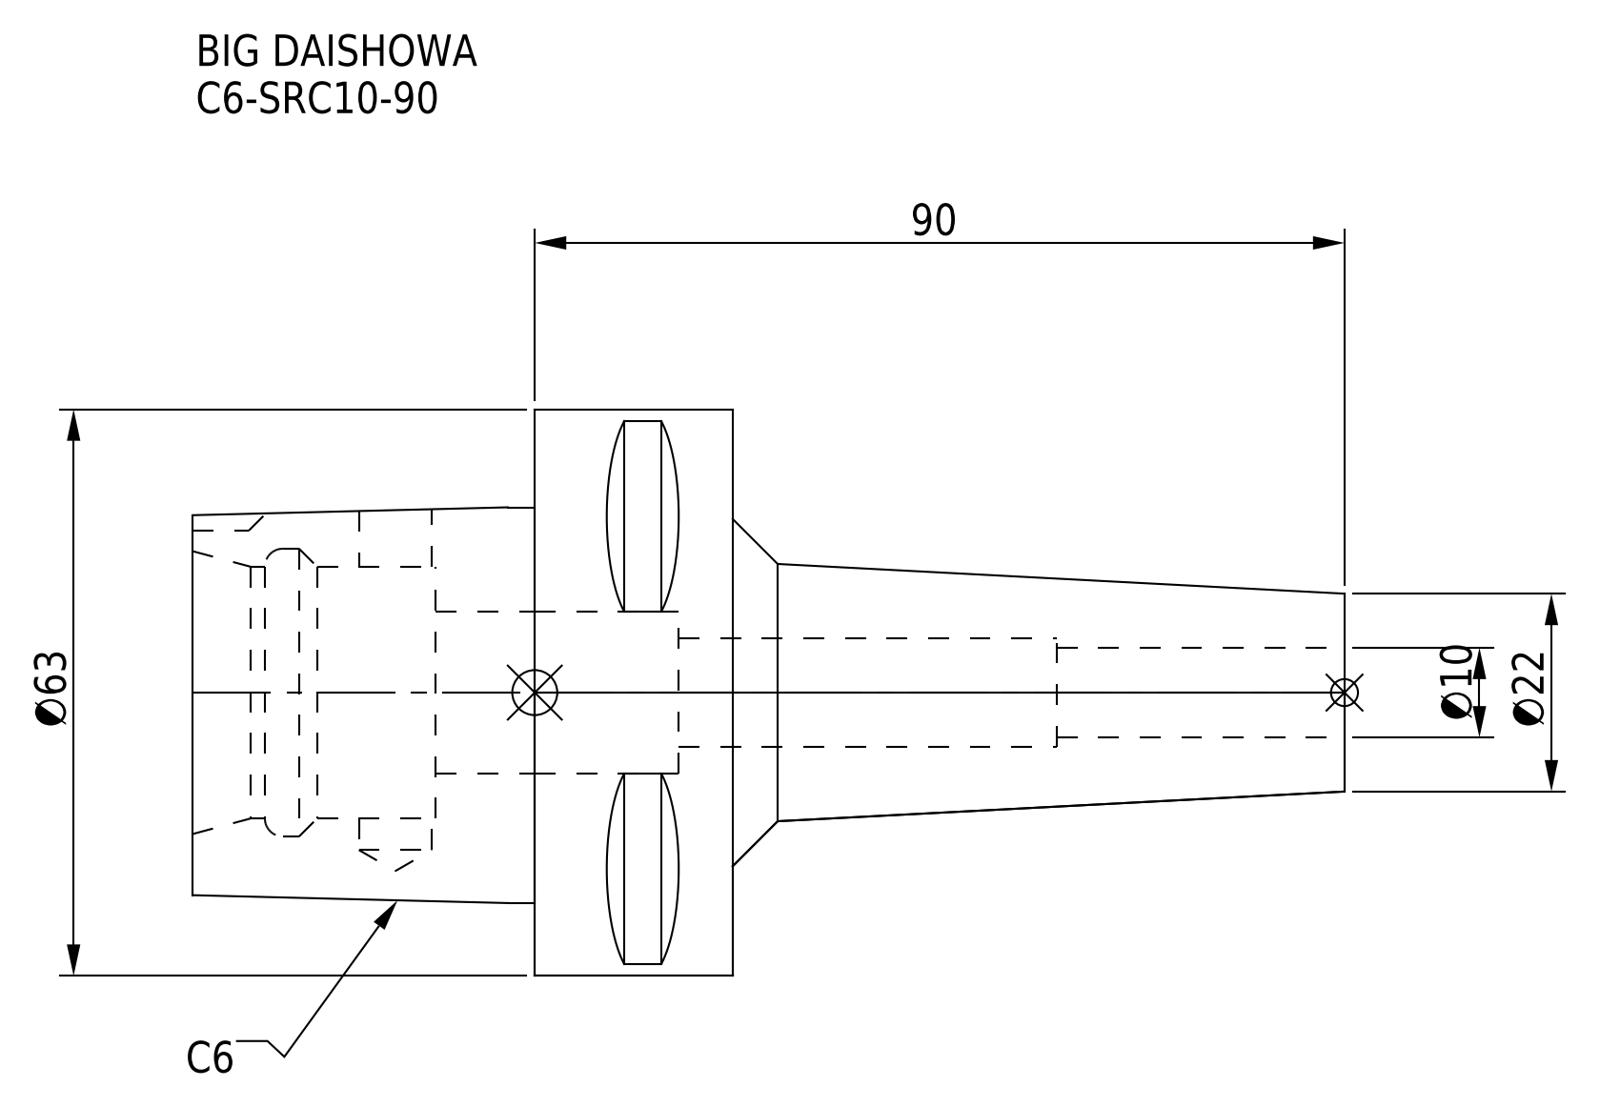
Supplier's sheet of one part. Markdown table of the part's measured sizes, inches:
| quantity | value |
| --- | --- |
| part name | C6-SRC10-90 |
| STEP written by | CREO PARAMETRIC BY PTC INC, 2016380 (AUTOMOTIVE_DESIGN) |
| units | inches |
| bodies | 1 solid, 62 faces (29 planar, 19 cylindrical, 14 other) |
| overall size | 5.039 × 2.48 × 2.48 |
| volume | 7.667 in³ |
| surface area | 42.71 in² |
| round holes (diameter × count) | 0.319 × 1, 0.394 × 1, 0.472 × 1, 0.709 × 1, 1.102 × 1, 1.26 × 1 |
| round bosses / shafts (diameter × count) | 2.48 × 1 |
| partial cylindrical surfaces (radius × count) | 0.197 × 1 |
| main face-to-face distances | 0.866, 1.063, 2.362, 1.496, 1.299, 0.433, 2.677, 3.543, 3.976, 5.039 |
